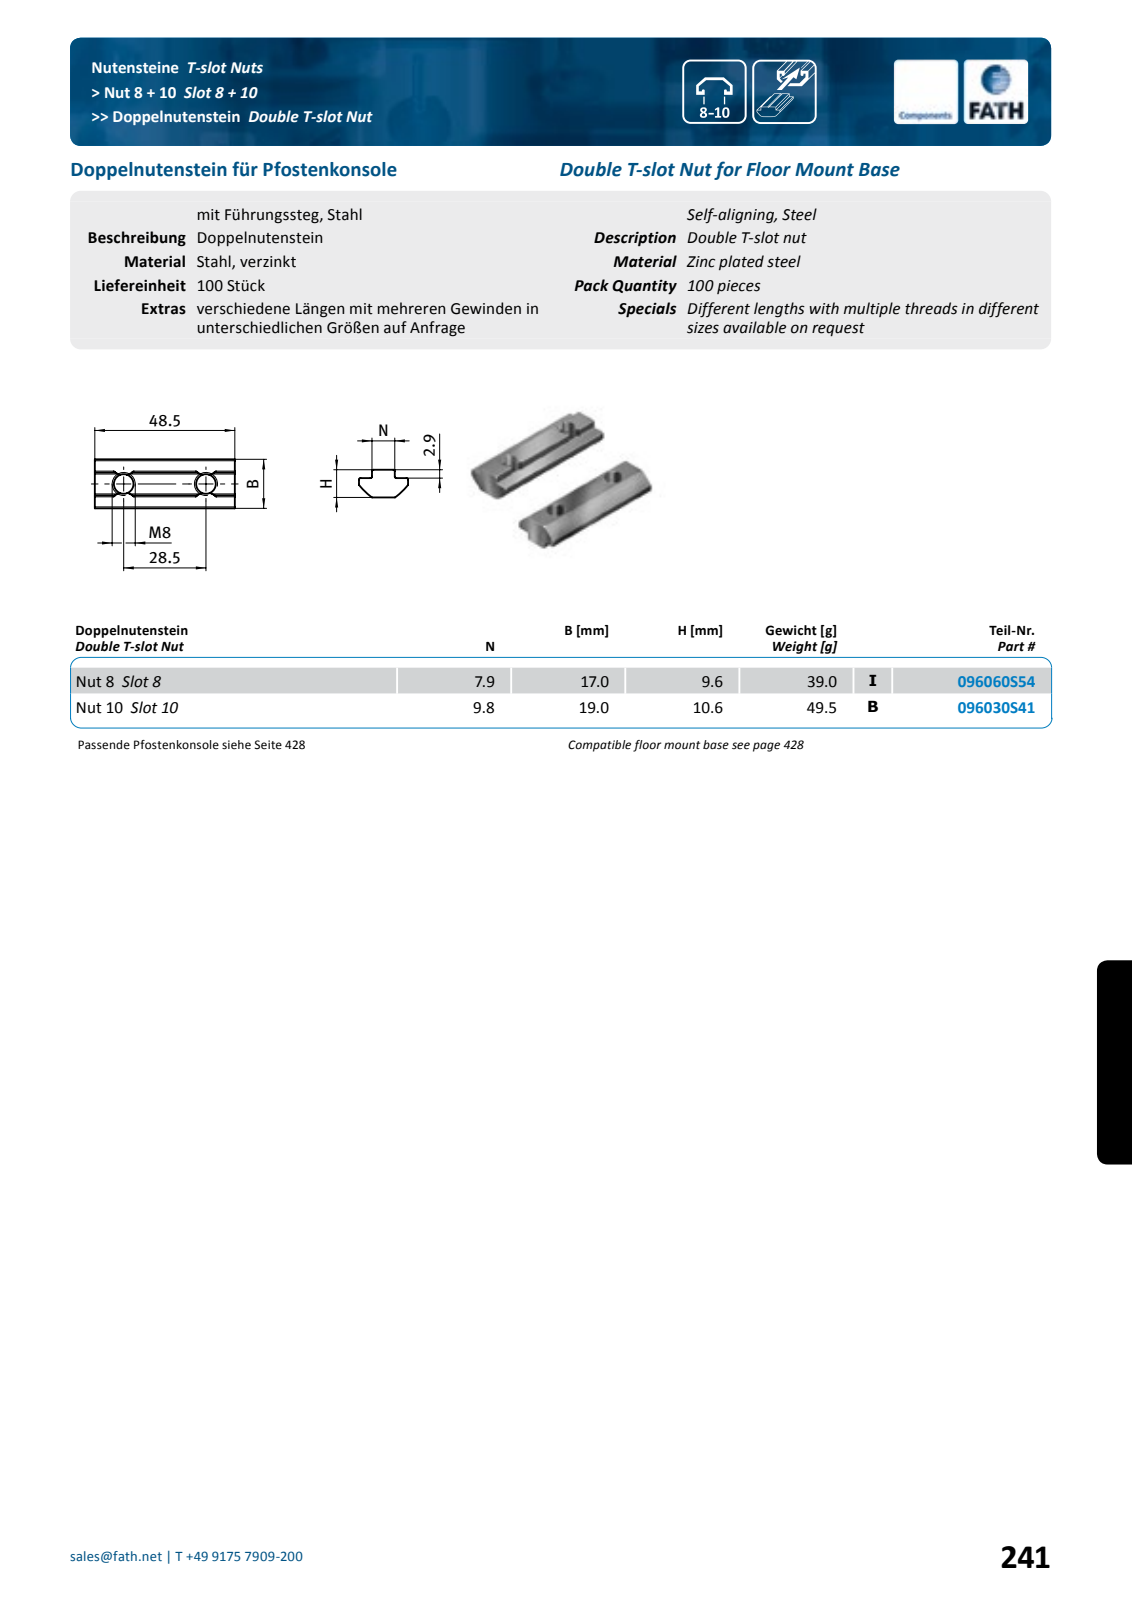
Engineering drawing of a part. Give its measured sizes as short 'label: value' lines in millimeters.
name: fath_096060s54
written by: Spatial InterOp 3D (automotive_design)
unit: mm
bodies: 1 solid, 46 faces (16 planar, 30 cylindrical, 0 other)
size: 48.5 × 17 × 9.6
volume: 5 029 mm³; area: 2 726 mm²
holes: 2× ⌀6.8
rounds: 6× R0.5, 4× R5, 2× R0.17, 2× R24.5
face distances: 6.7, 9.6, 2.9, 48.5, 17, 12.4, 4.6, 4.5, 7.9, 12.5
hole spacings: 28.5
